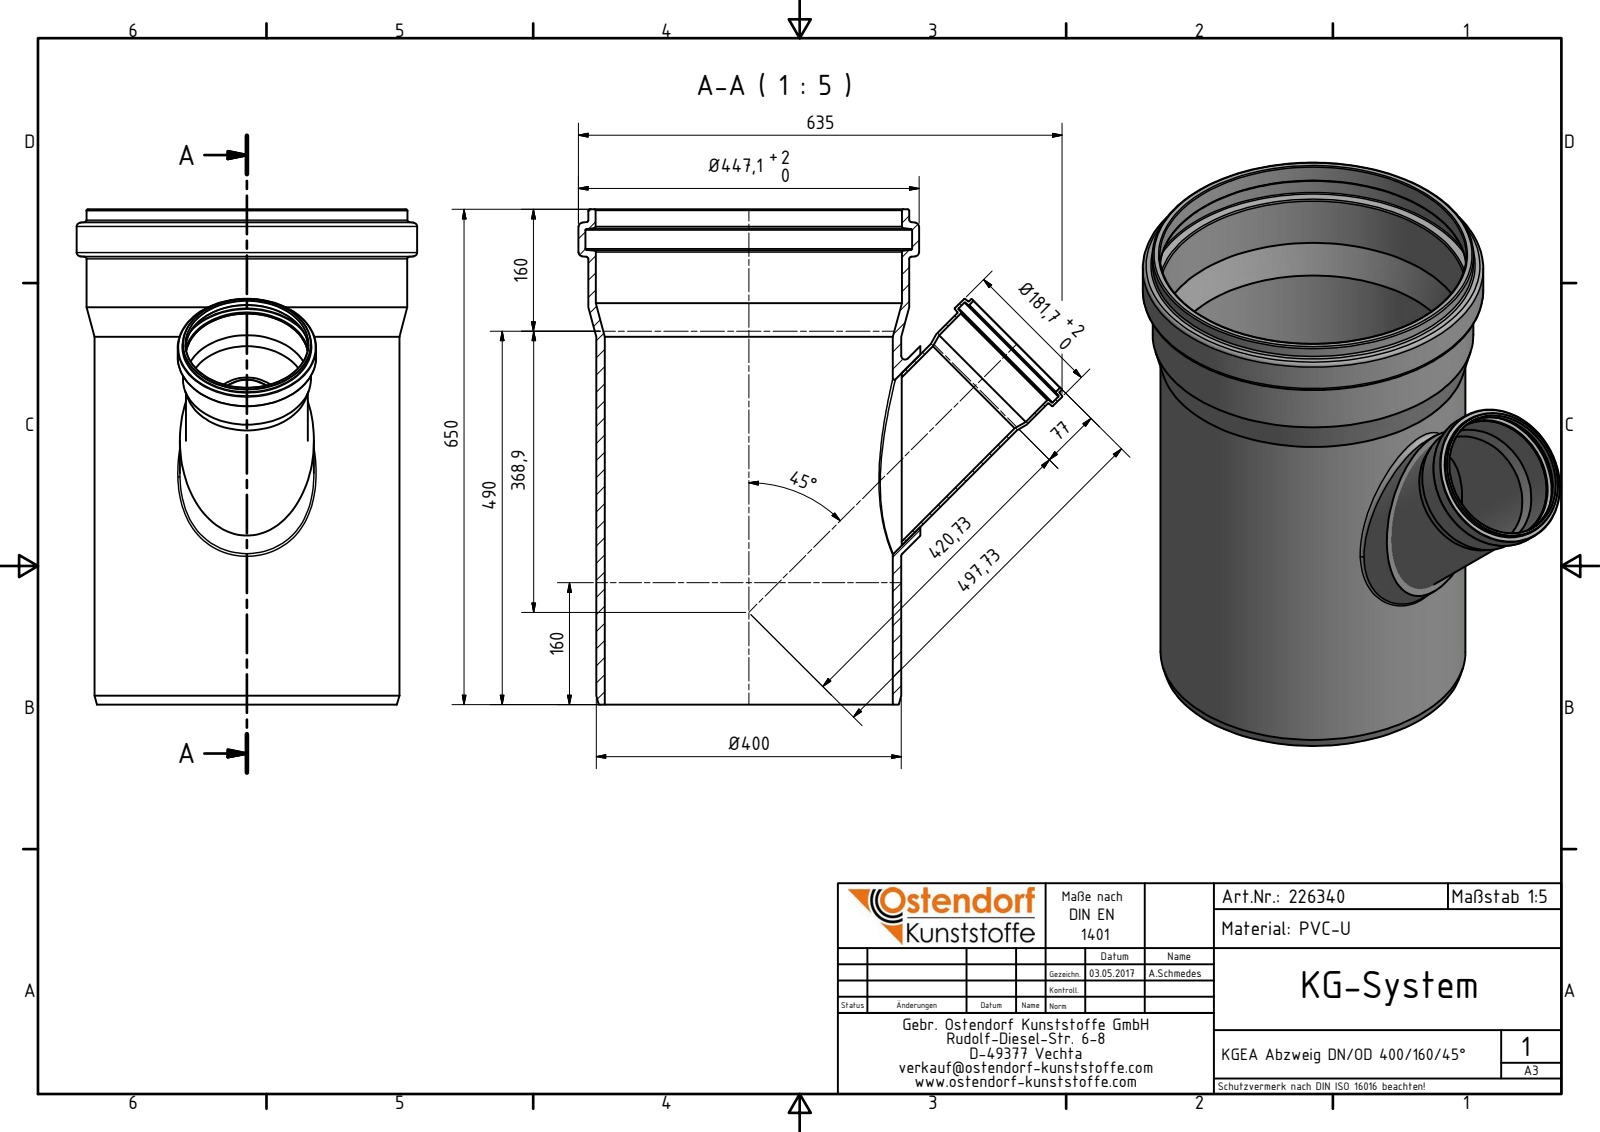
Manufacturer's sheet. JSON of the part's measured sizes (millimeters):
{"part_name": "226340 KGEA Abzweig DN_OD 400_160_45°; 226340 KGEA Abzweig DN_OD 400_160_45° Abzweig", "step_written_by": "Autodesk Inventor 2016 (AUTOMOTIVE_DESIGN)", "units": "millimeters", "bodies": {"solids": 2, "faces": 60, "planar": 6, "cylindrical": 19, "other": 35}, "overall_size": [651.35, 650, 447.1], "volume_mm3": 9200000, "surface_area_mm2": 1924000, "round_holes": [[152.15, 1], [160, 1], [160.75, 1], [161, 1], [174.5, 1], [378.35, 1], [402, 1], [402.4, 1], [429.1, 1]], "round_bosses_or_shafts": [[447.1, 1], [421.4, 1], [421.1, 1], [400.35, 1], [181.7, 1], [176, 1], [168.2, 1], [167.95, 1]], "face_to_face_distances": [650, 24.5, 23.6]}
